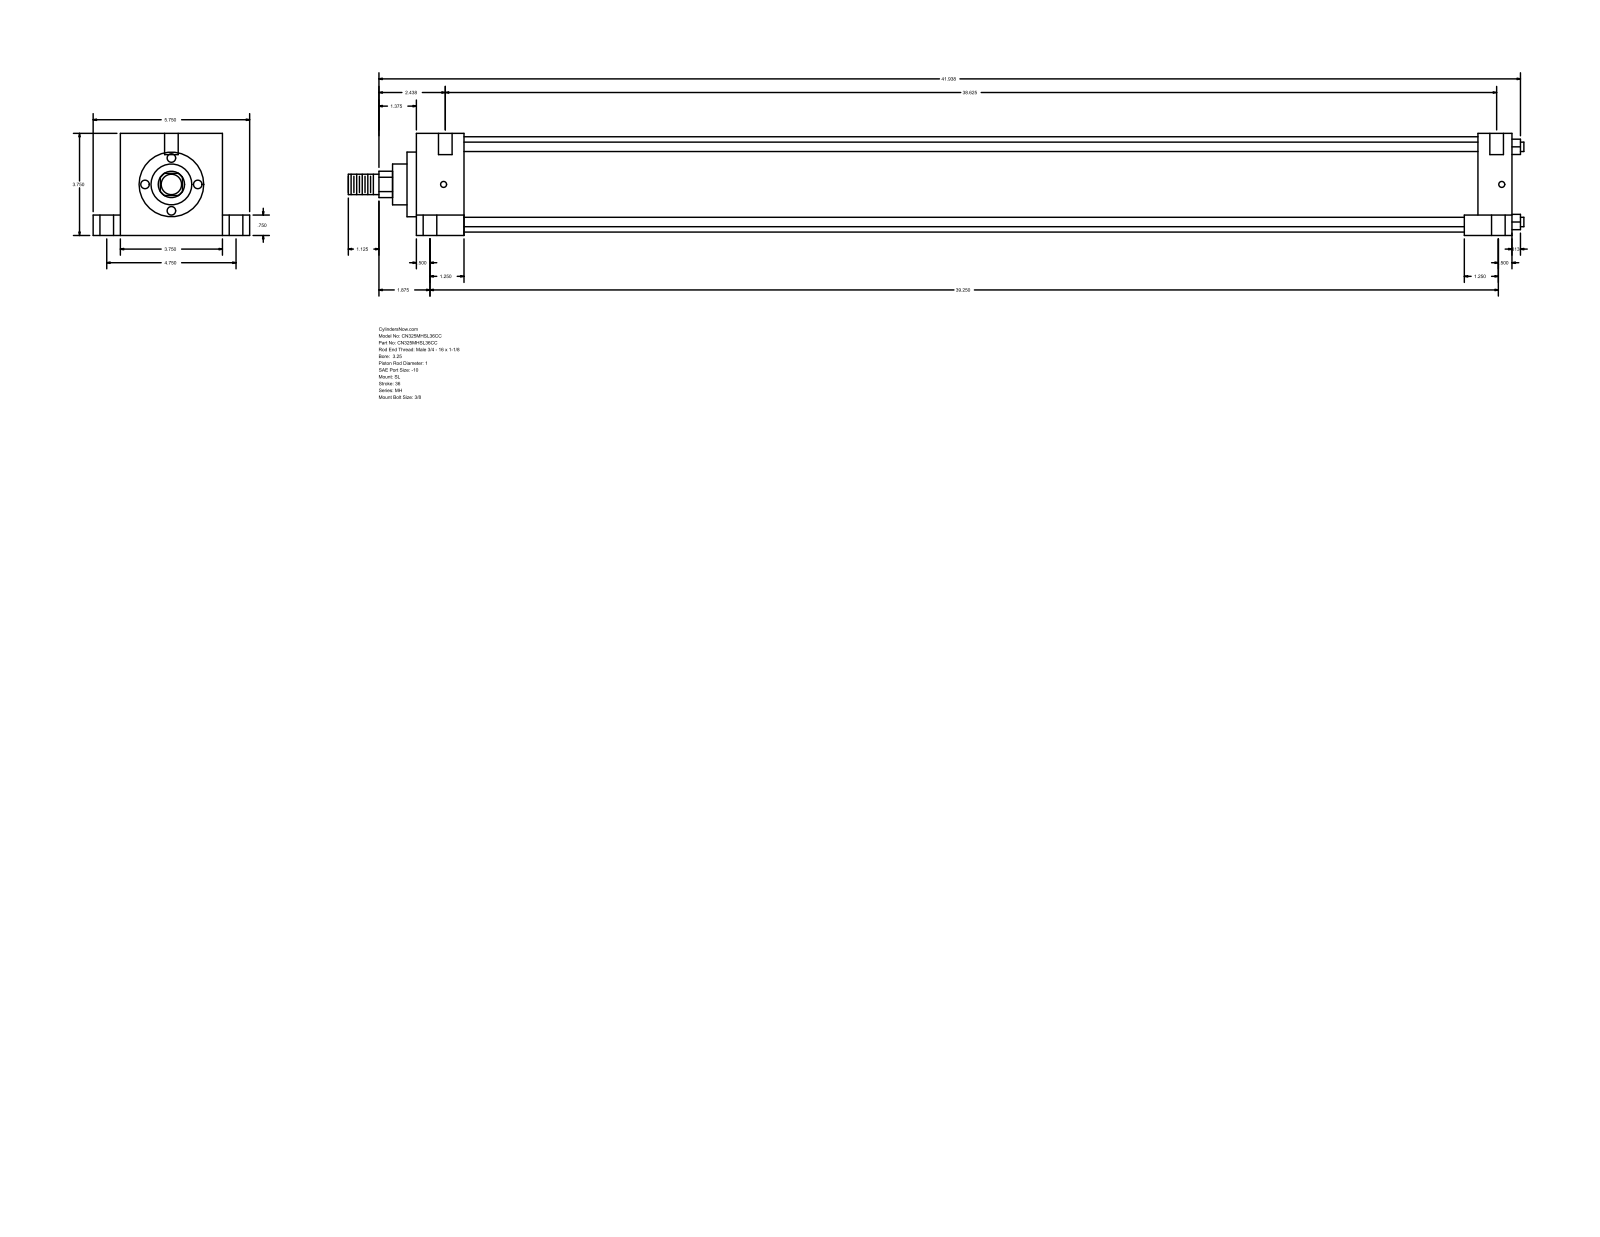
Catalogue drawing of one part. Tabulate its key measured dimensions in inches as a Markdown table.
| quantity | value |
| --- | --- |
| part name | MH_SL__0325_1 |
| STEP written by | GSSL Pune (CONFIG_CONTROL_DESIGN) |
| units | inches |
| bodies | 0 solids, 110 faces (77 planar, 33 cylindrical, 0 other) |
| overall size | 43.187 × 5.75 × 3.75 |
| round holes (diameter × count) | 0.5 × 6, 0.219 × 4, 0.75 × 4 |
| round bosses / shafts (diameter × count) | 0.345 × 4, 3.5 × 1, 2.375 × 1, 1.5 × 1, 1 × 1, 0.75 × 1 |
| partial cylindrical surfaces (radius × count) | 0.484 × 1 |
| main face-to-face distances | 3.75, 40.25, 1.75, 38.5, 1, 4.75, 0.75, 3, 39, 37.25 |
| hole center spacings | 2.376, 2.378, 2.427, 2.441, 4.75, 38.761, 38.823, 38.875 |
